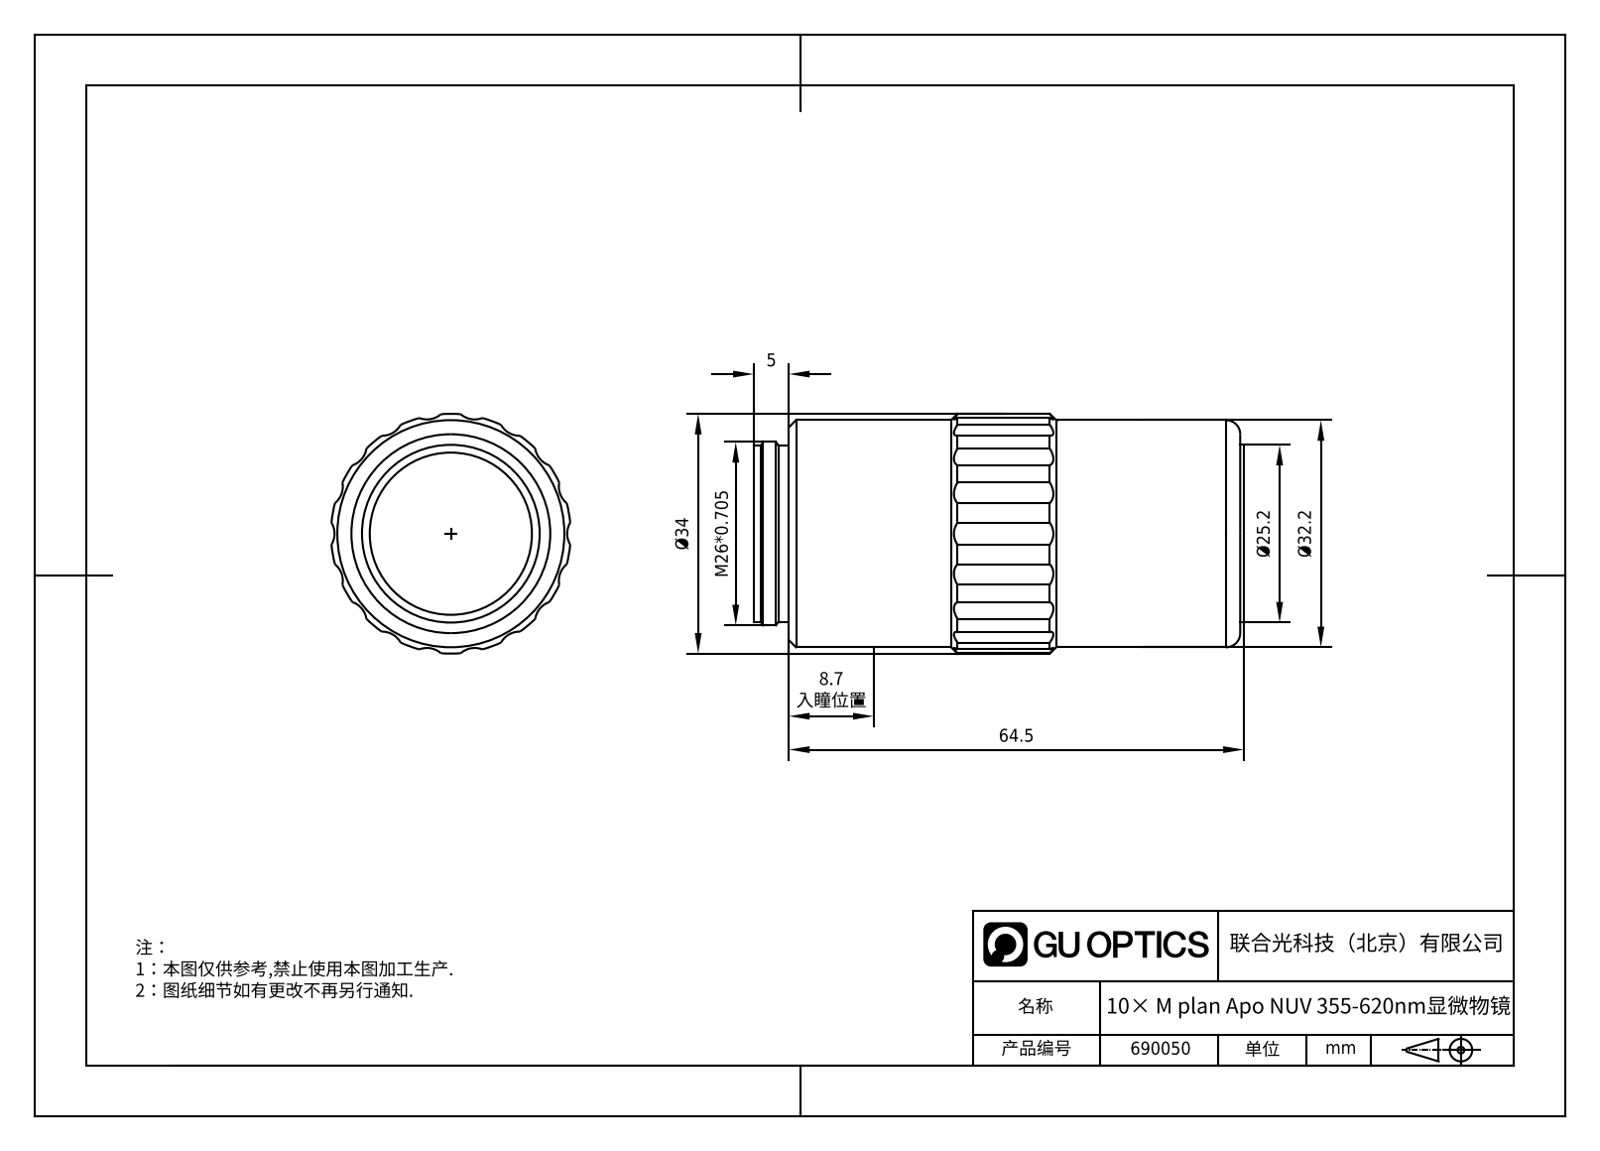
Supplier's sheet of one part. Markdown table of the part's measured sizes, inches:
| quantity | value |
| --- | --- |
| part name | 690050 |
| STEP written by | SolidWorks 2020 (CONFIG_CONTROL_DESIGN) |
| units | inches |
| bodies | 1 solid, 57 faces (7 planar, 44 cylindrical, 6 other) |
| overall size | 2.736 × 1.339 × 1.333 |
| volume | 3.387 in³ |
| surface area | 13.49 in² |
| round holes (diameter × count) | 0.492 × 1, 0.906 × 1 |
| round bosses / shafts (diameter × count) | 1.268 × 1, 1.024 × 1, 0.992 × 1, 0.984 × 1 |
| partial cylindrical surfaces (radius × count) | 0.118 × 18, 0.669 × 1 |
| main face-to-face distances | 2.717, 0.197, 2.52, 0.039, 0.157, 2.677, 2.736, 2.697, 2.539, 0.02 |
